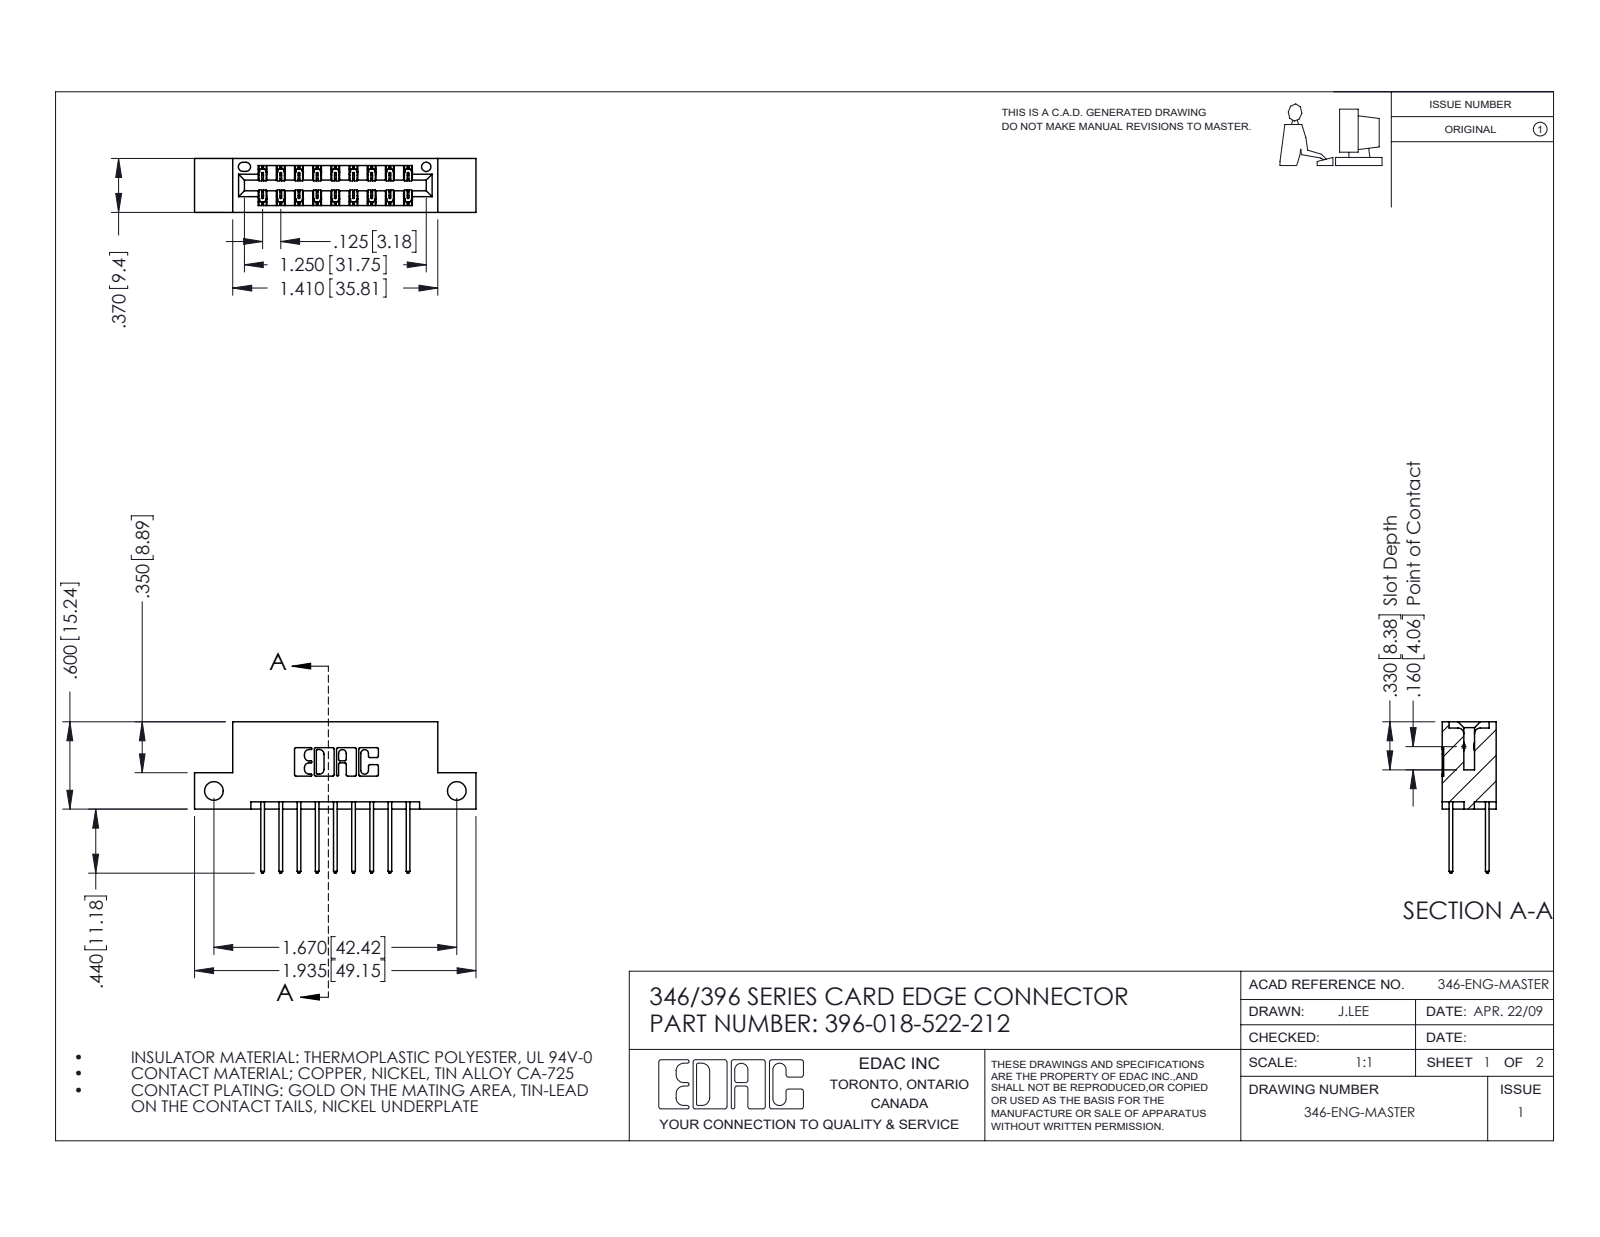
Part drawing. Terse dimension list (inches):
name: 345-292-001_345-293-122; 346 Part_Flush Mounting Lugs - Side Mount; 396-018-522-212
written by: SolidWorks 2016 (CONFIG_CONTROL_DESIGN)
unit: in
bodies: 19 solids, 1058 faces (706 planar, 352 cylindrical, 0 other)
size: 1.935 × 1.04 × 0.37
volume: 0.274 in³; area: 8.892 in²
holes: 2× ⌀0.128, 1× ⌀0.064
rounds: 27× R0.006, 22× R0.01, 18× R0.01, 6× R0.007, 6× R0.031, 3× R0.026, 2× R0.014, 2× R0.022
face distances: 0.25, 0.048, 0.322, 0.37, 0.072, 0.298, 0.025, 0.275, 0.148, 0.222
hole spacings: 1.67
